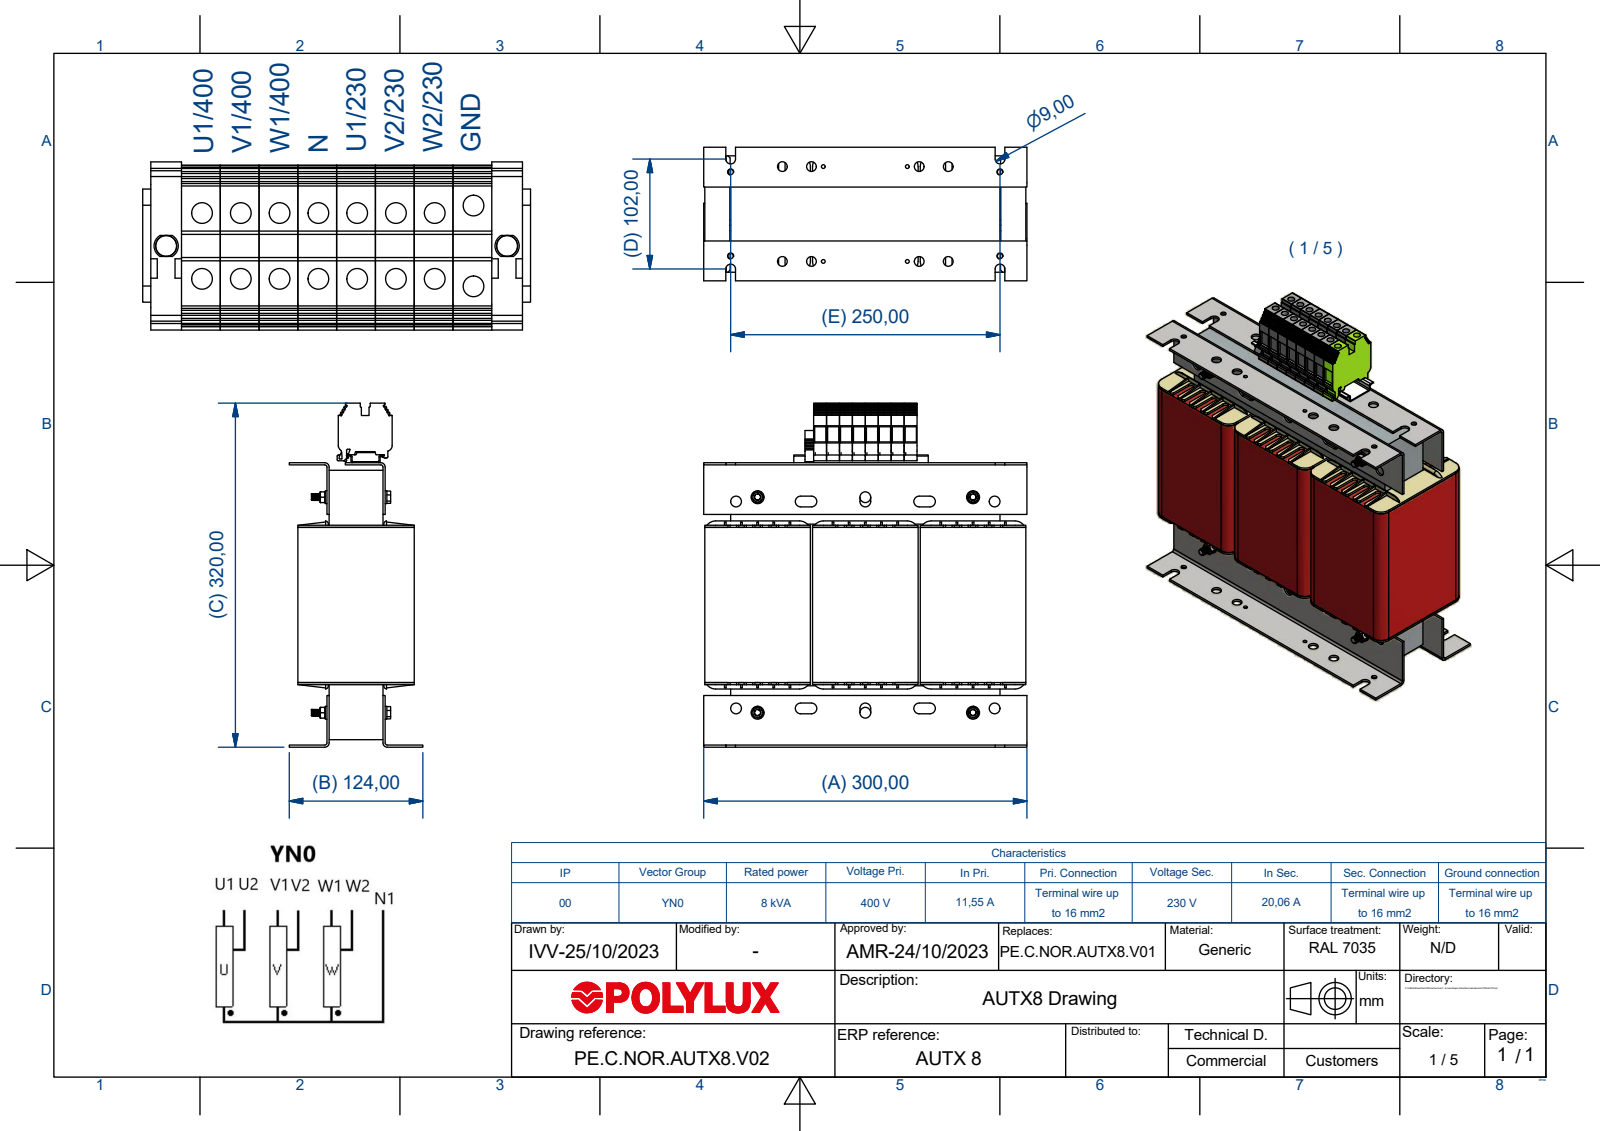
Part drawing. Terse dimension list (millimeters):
name: AUTX8
written by: Autodesk Inventor 2018 (AUTOMOTIVE_DESIGN)
unit: mm
bodies: 0 solids, 2029 faces (1480 planar, 505 cylindrical, 44 other)
size: 319.3 × 300 × 124
holes: 16× ⌀6.4, 10× ⌀9, 6× ⌀4.92, 6× ⌀10, 4× ⌀3.5, 1× ⌀5.8
bosses: 4× ⌀12, 4× ⌀6
rounds: 48× R0.5, 28× R3, 12× R5, 12× R10, 11× R1, 6× R2, 6× R4.5, 5× R0.2
face distances: 2, 50, 58, 204, 29, 79, 27, 100, 52, 81
hole spacings: 12, 23.62, 48.26, 88, 202.06, 11, 20.35, 24
